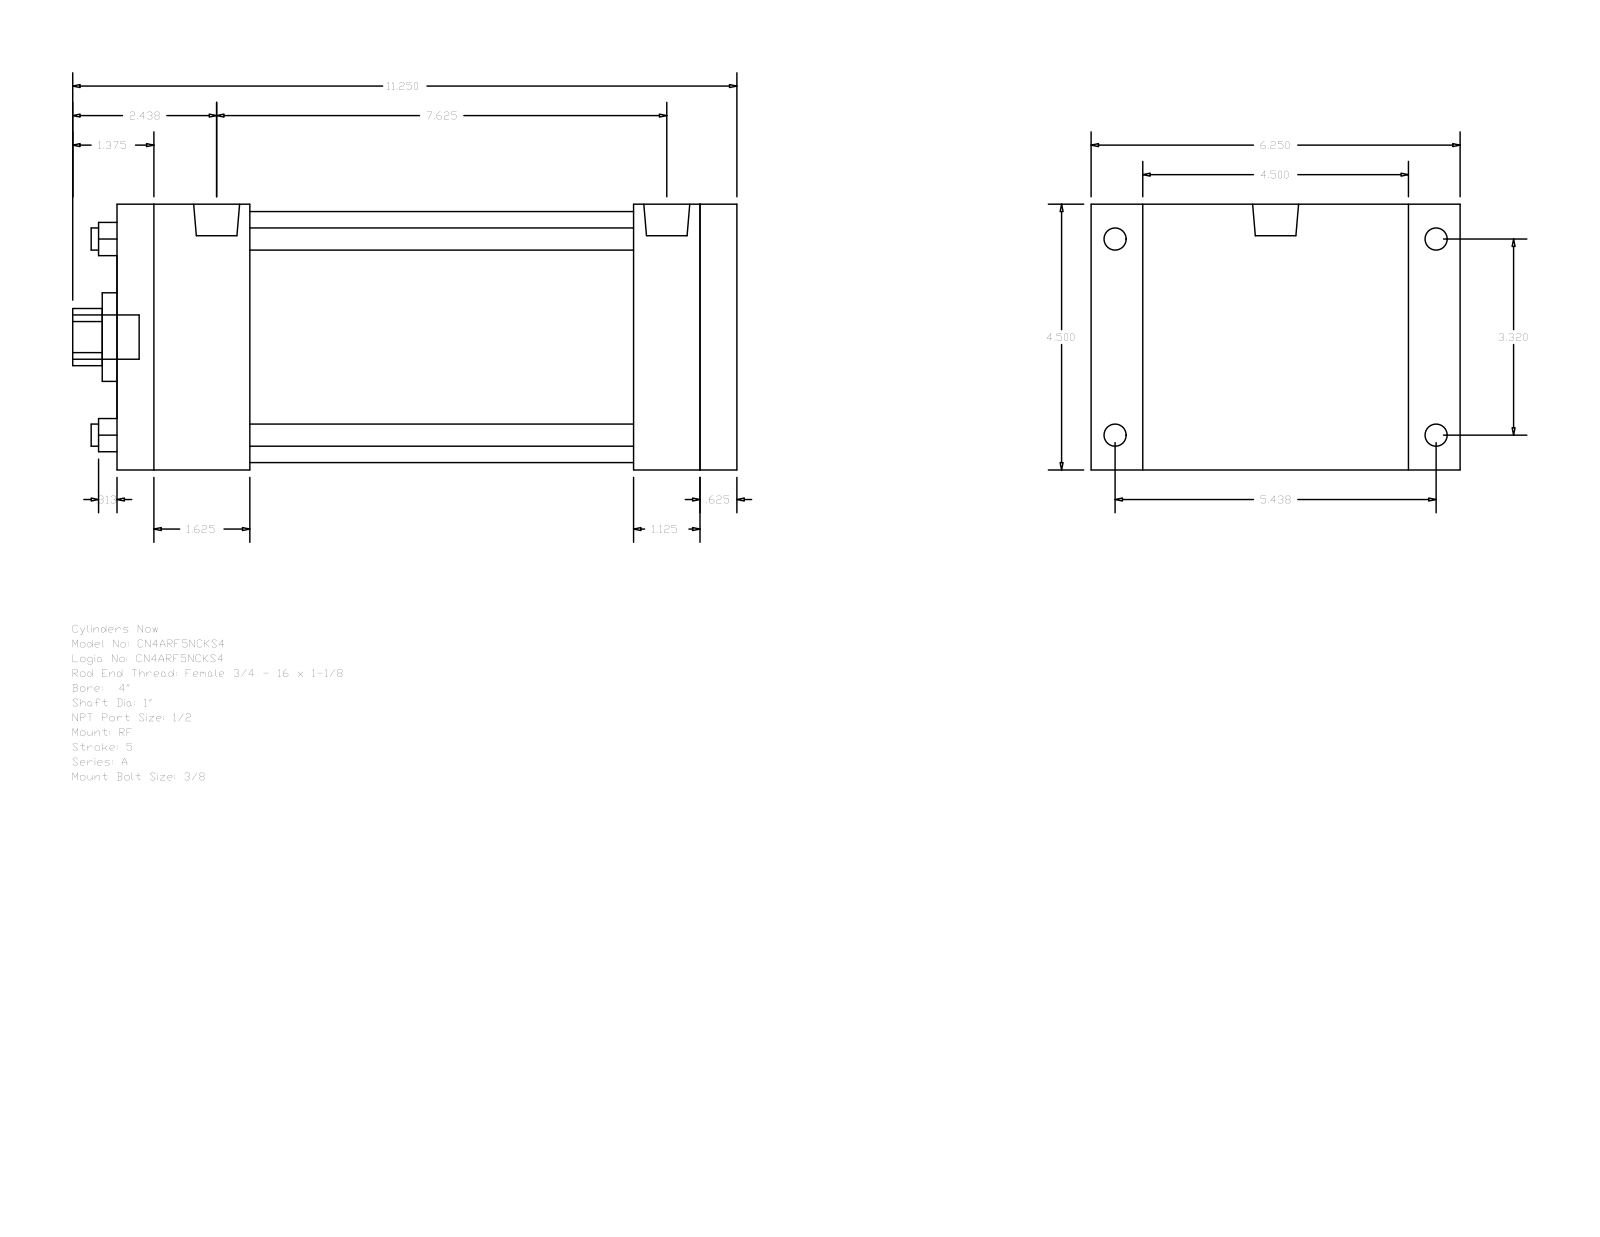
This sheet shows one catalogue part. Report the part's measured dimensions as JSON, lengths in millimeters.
{"part_name": "A_RF__0400_1", "step_written_by": "GSSL Pune (CONFIG_CONTROL_DESIGN)", "units": "millimeters", "bodies": {"solids": 0, "faces": 92, "planar": 64, "cylindrical": 28, "other": 0}, "overall_size": [285.75, 158.75, 114.3], "round_holes": [[9.53, 4], [25.4, 1], [38.1, 1], [107.95, 1]], "round_bosses_or_shafts": [[9.53, 4], [8.73, 4], [19.77, 2], [19.05, 1]], "partial_cylinders_radius": [[12.29, 1]], "face_to_face_distances": [114.3, 266.7, 15.87, 250.83, 22.23, 136.53, 222.25, 28.58, 44.45, 57.15], "hole_center_spacings": [59.62, 84.32, 119.25]}
